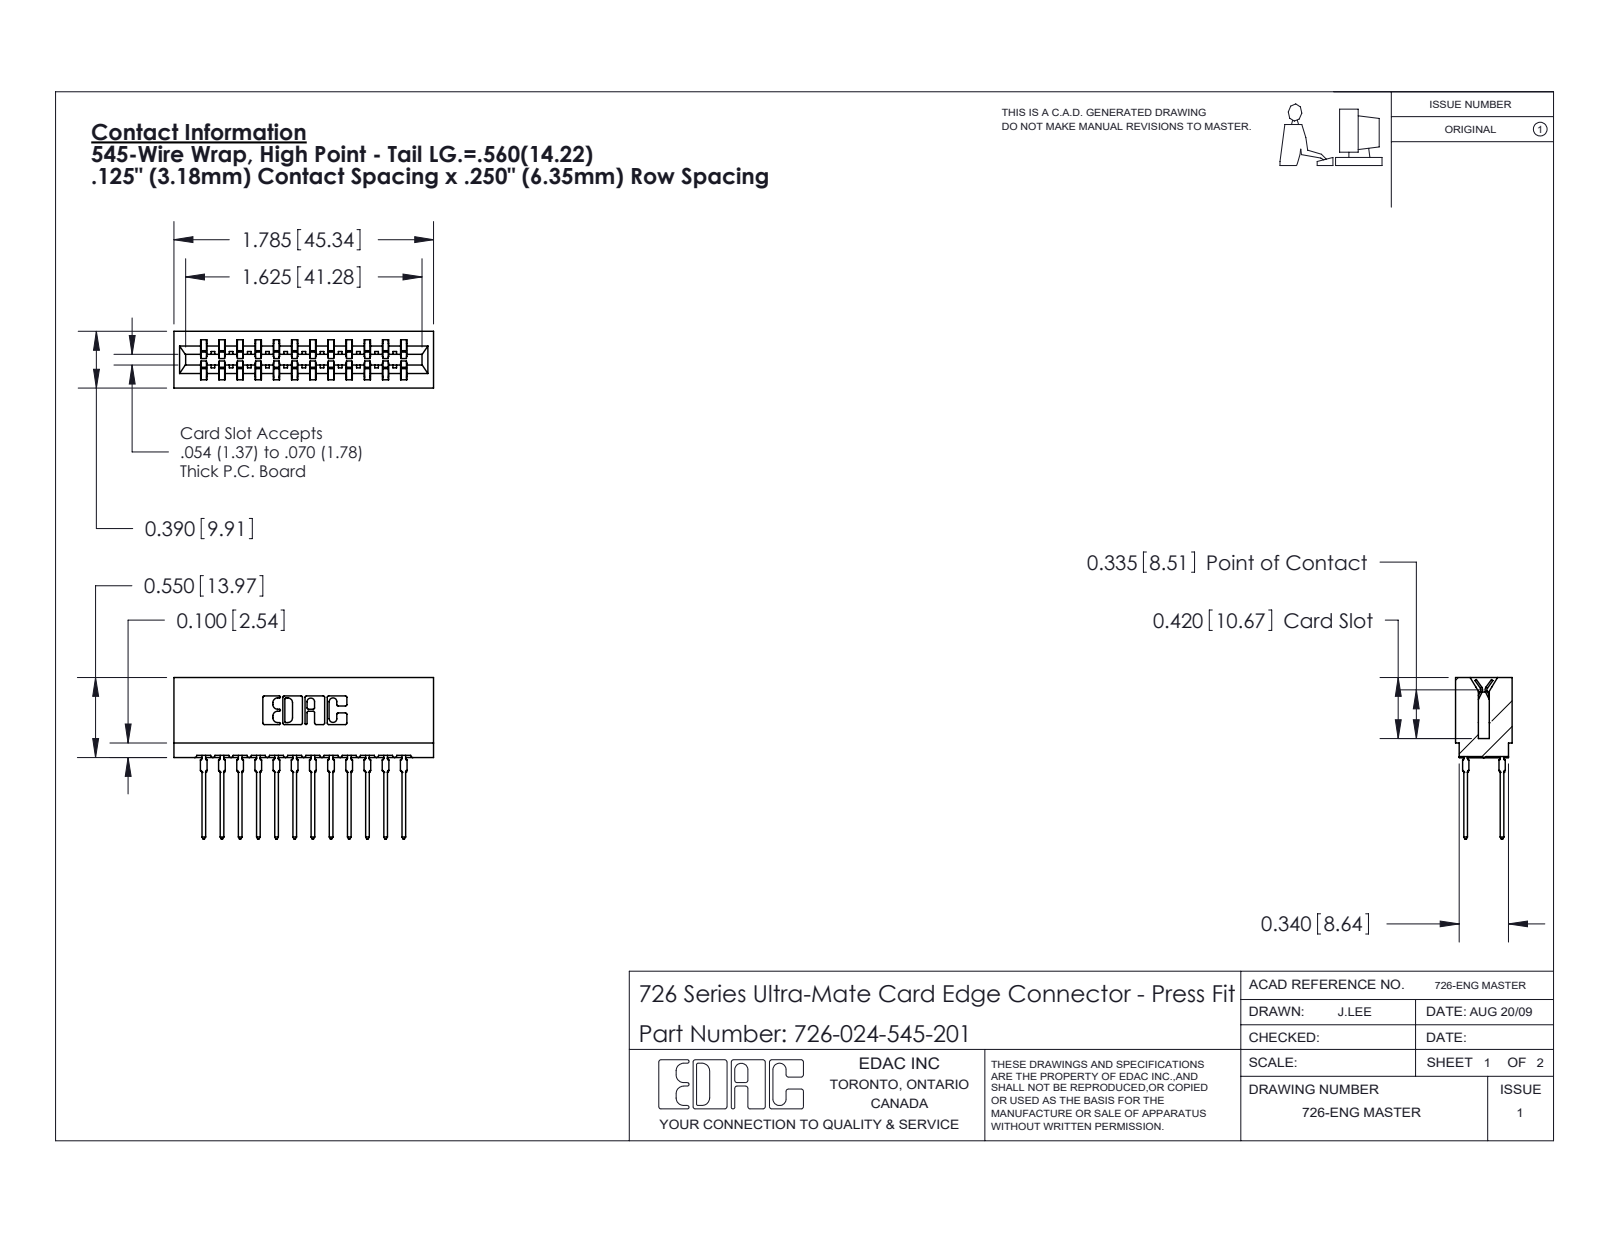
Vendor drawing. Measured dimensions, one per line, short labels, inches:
name: 746-292-001_545; 726 Part_.515 Slot Depth - 01; 726-024-545-201
written by: SolidWorks 2020 (CONFIG_CONTROL_DESIGN)
unit: in
bodies: 25 solids, 2245 faces (1159 planar, 462 cylindrical, 624 other)
size: 1.785 × 1.109 × 0.39
volume: 0.269 in³; area: 11.17 in²
rounds: 48× R0.021, 22× R0.01, 13× R0.015, 8× R0.005, 8× R0.011, 6× R0.007, 6× R0.031, 3× R0.026
face distances: 0.25, 0.057, 0.333, 0.5, 0.025, 0.307, 0.083, 0.39, 0.125, 0.75
